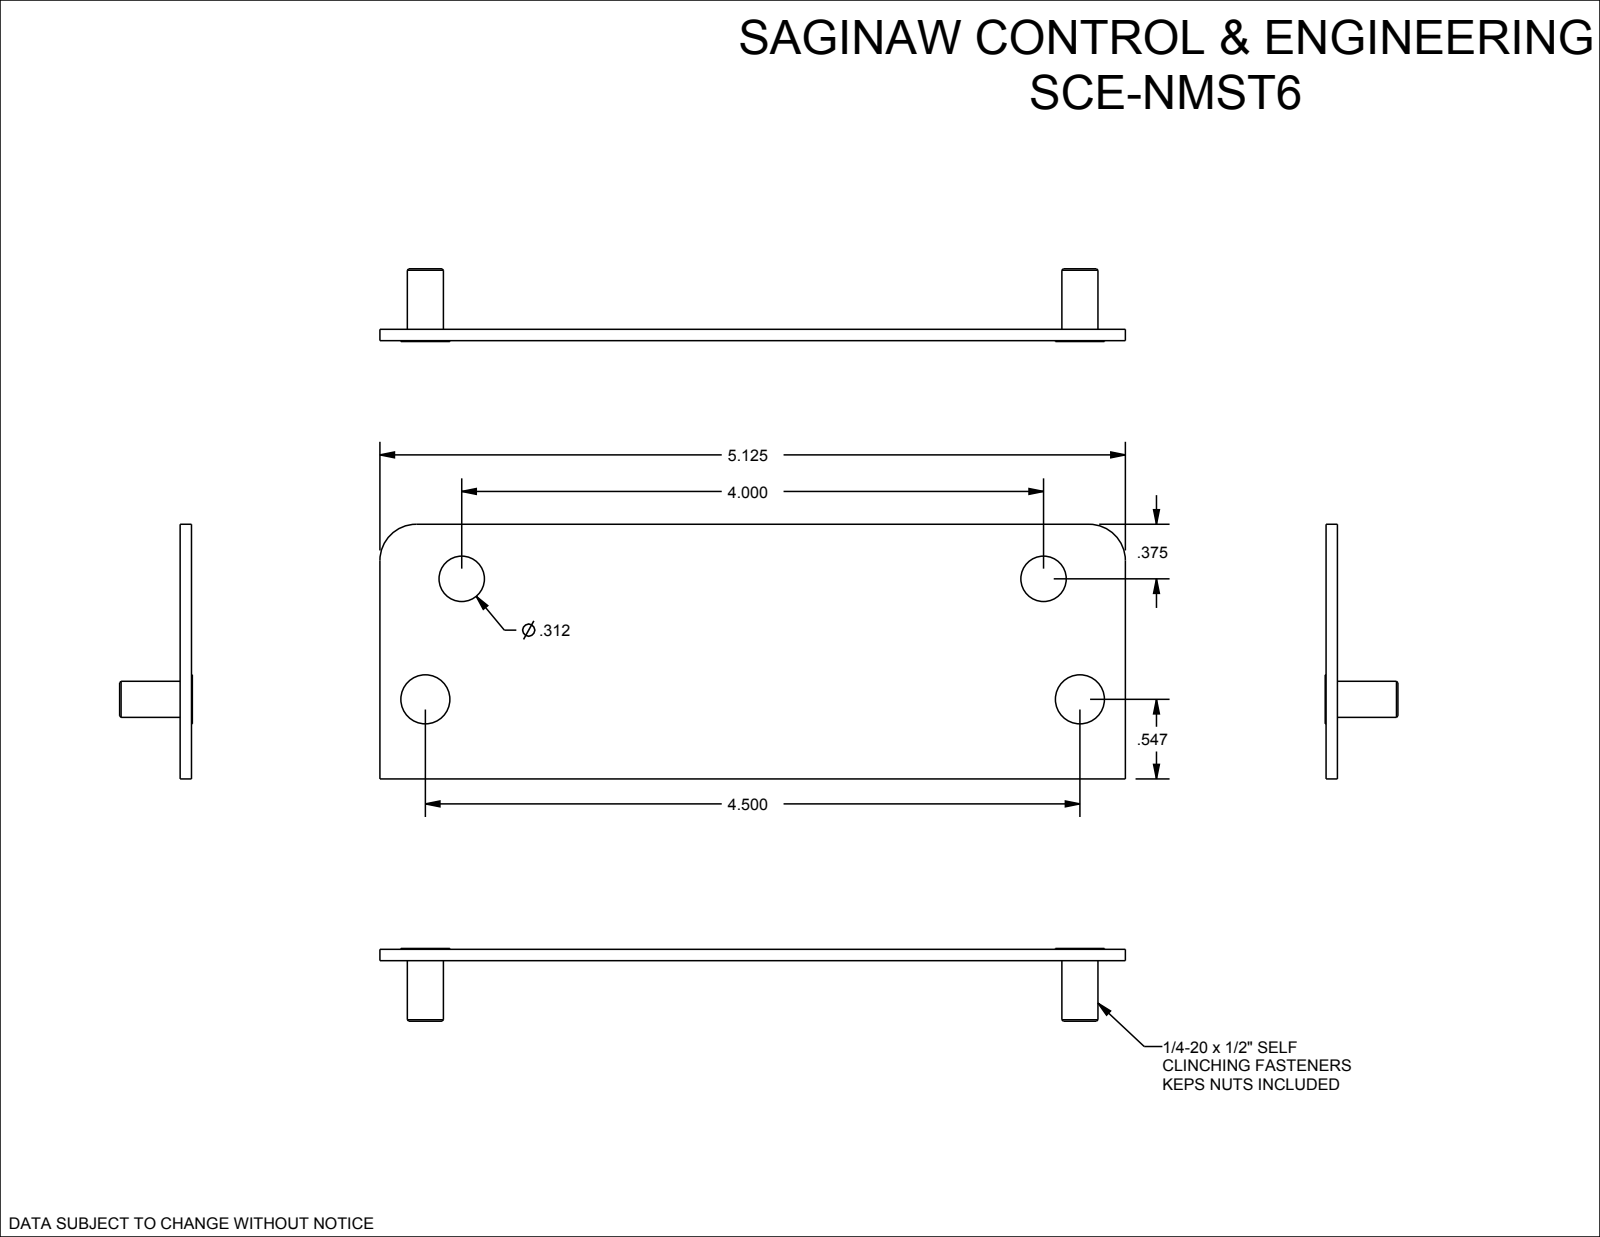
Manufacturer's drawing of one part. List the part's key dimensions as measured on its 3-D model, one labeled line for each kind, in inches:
Part name (STEP PRODUCT): SCE-NMST6
STEP written by: SolidWorks 2019 (AUTOMOTIVE_DESIGN)
Units: inches
Bodies: 3 solids, 24 faces (12 planar, 10 cylindrical, 2 other)
Overall size (bounding box): 5.125 × 1.75 × 0.5
Volume: 0.728 in³ · Surface area: 19.85 in²
Round holes (diameter × count): ⌀0.25 ×2, ⌀0.312 ×2
Round bosses / shafts (diameter × count): ⌀0.337 ×2, ⌀0.248 ×2
Partial cylindrical surfaces — rounded edges, fillets, slot ends (radius × count): R0.25 ×2
Main face-to-face distances: 0.078, 1.75, 0.084, 5.125, 0.066, 0.018, 0.416, 0.482, 0.494, 0.5
Hole centre spacings: 0.865, 4.33, 4, 4.5
